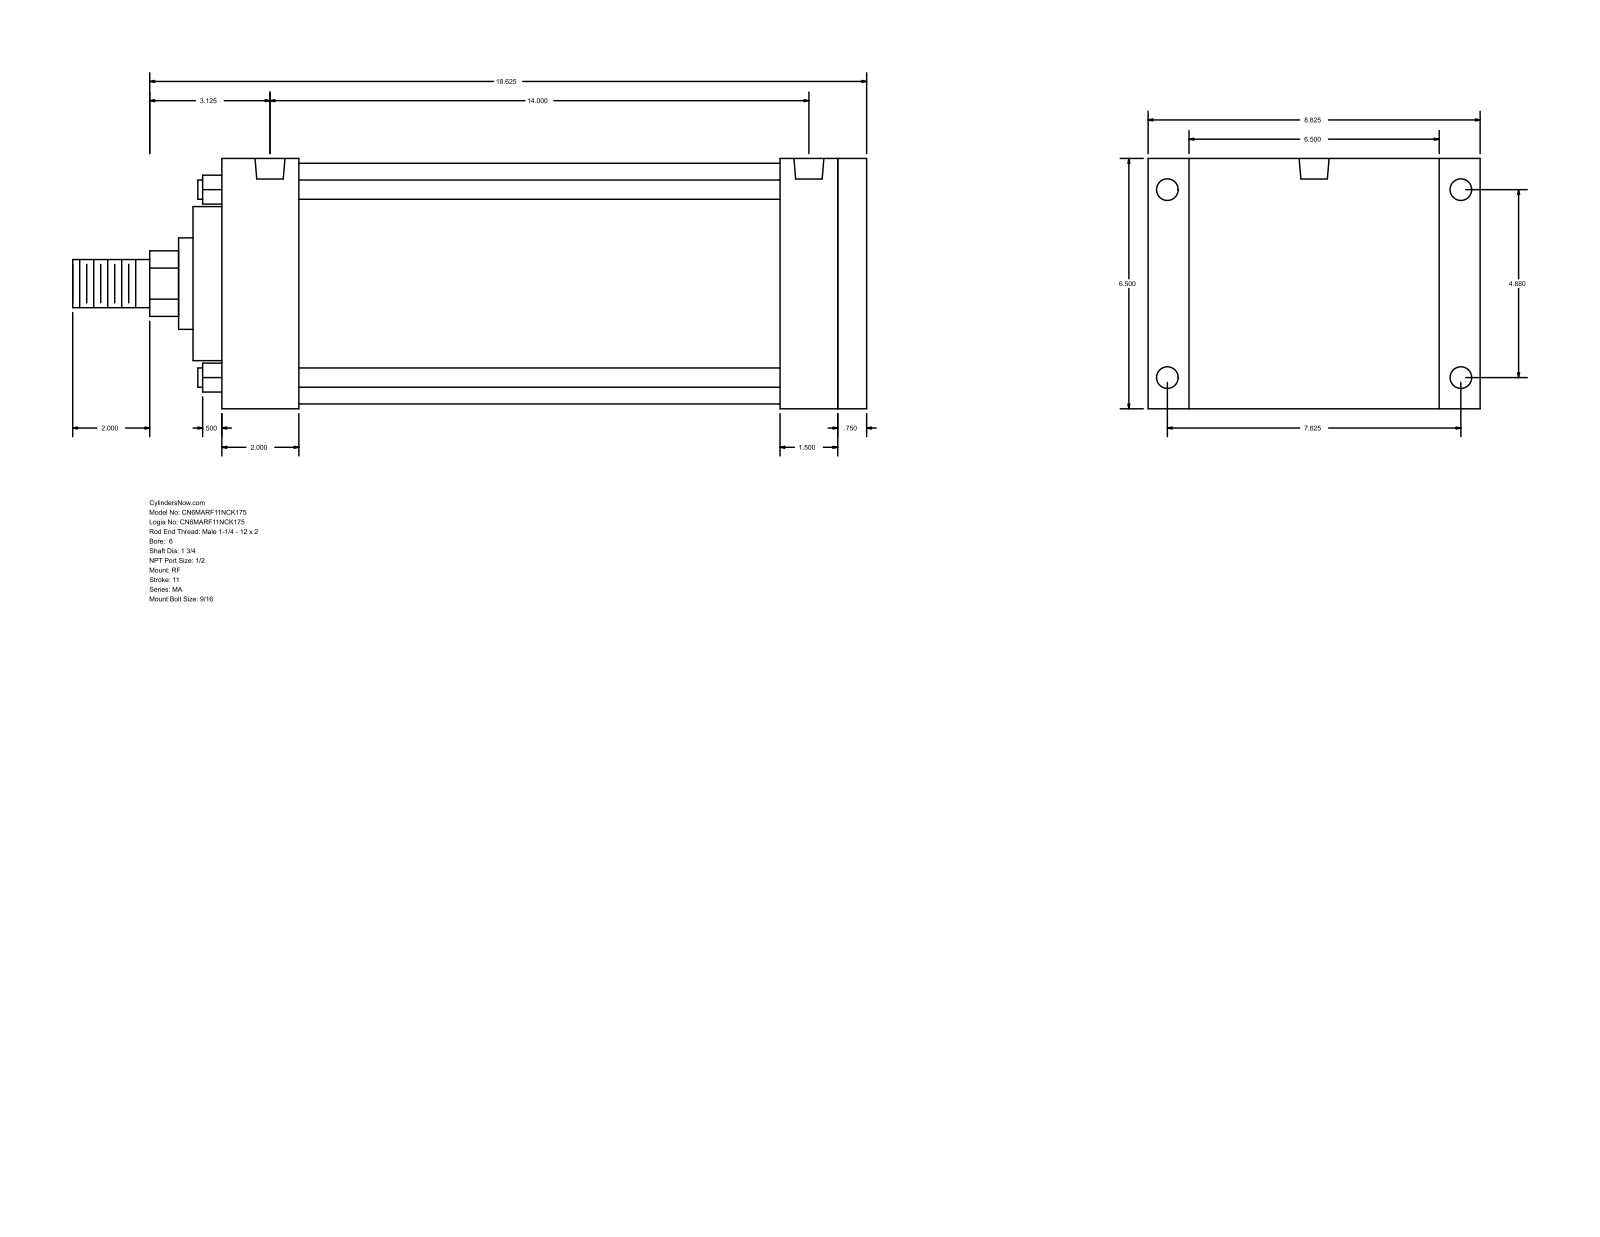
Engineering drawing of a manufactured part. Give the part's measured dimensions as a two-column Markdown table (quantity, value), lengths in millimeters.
| quantity | value |
| --- | --- |
| part name | MA_RF__0600_1.75 |
| STEP written by | GSSL Pune (CONFIG_CONTROL_DESIGN) |
| units | millimeters |
| bodies | 0 solids, 94 faces (65 planar, 29 cylindrical, 0 other) |
| overall size | 523.88 × 219.07 × 165.1 |
| round holes (diameter × count) | 14.29 × 4, 17.46 × 4, 19.77 × 2 |
| round bosses / shafts (diameter × count) | 12.7 × 4, 158.75 × 1, 101.6 × 1, 60.33 × 1, 44.45 × 1, 31.75 × 1 |
| partial cylindrical surfaces (radius × count) | 21.63 × 1 |
| main face-to-face distances | 165.1, 425.45, 19.05, 406.4, 50.8, 355.6, 374.65, 368.31, 317.51, 38.09 |
| hole center spacings | 123.96, 193.68, 229.95, 355.6 |
